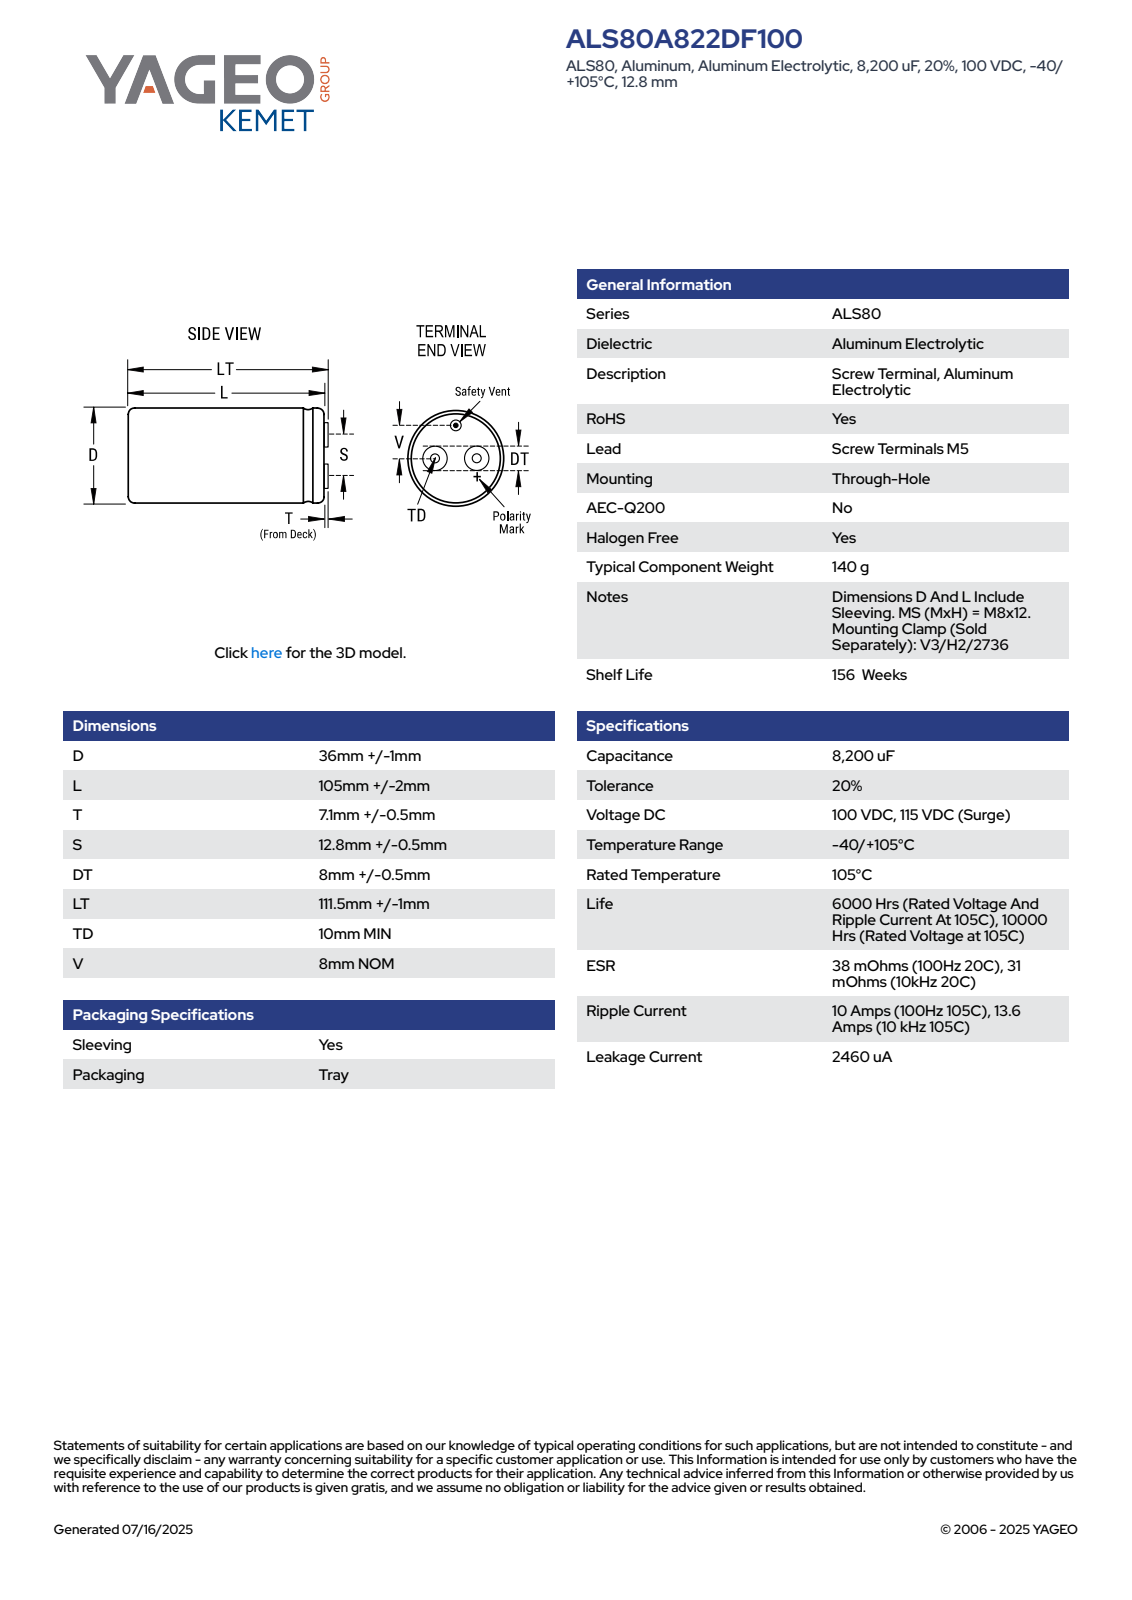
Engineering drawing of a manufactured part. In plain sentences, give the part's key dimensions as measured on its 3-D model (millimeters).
The part is named "CARC_KAR_36X105_D37L107T7.6S12.8DT8.500TD10.000V8.000". Its 3-D file was written by "SolidWorks 2014 (AUTOMOTIVE_DESIGN)". It is 1 solid with 88 faces: 30 planar, 19 cylindrical and 39 other. Overall it measures 114.6 by 37.01 by 37 millimeters. Its volume is 114 659 cubic millimeters and its surface area 15 149 square millimeters. Round holes: 2 of diameter 5, 1 of diameter 1.33. Round bosses or shafts: 2 of diameter 8.5, 1 of diameter 37, 1 of diameter 2.27. Partial cylindrical surfaces (rounded edges, fillets, slot ends): 1 of radius 18.51. The main face-to-face distances are 107, 114.6, 7.6, 104.6, 2.4, 10, 107.35, 2.75, 0.35, 7.25. The hole center spacings are 10.24, 12.8.
